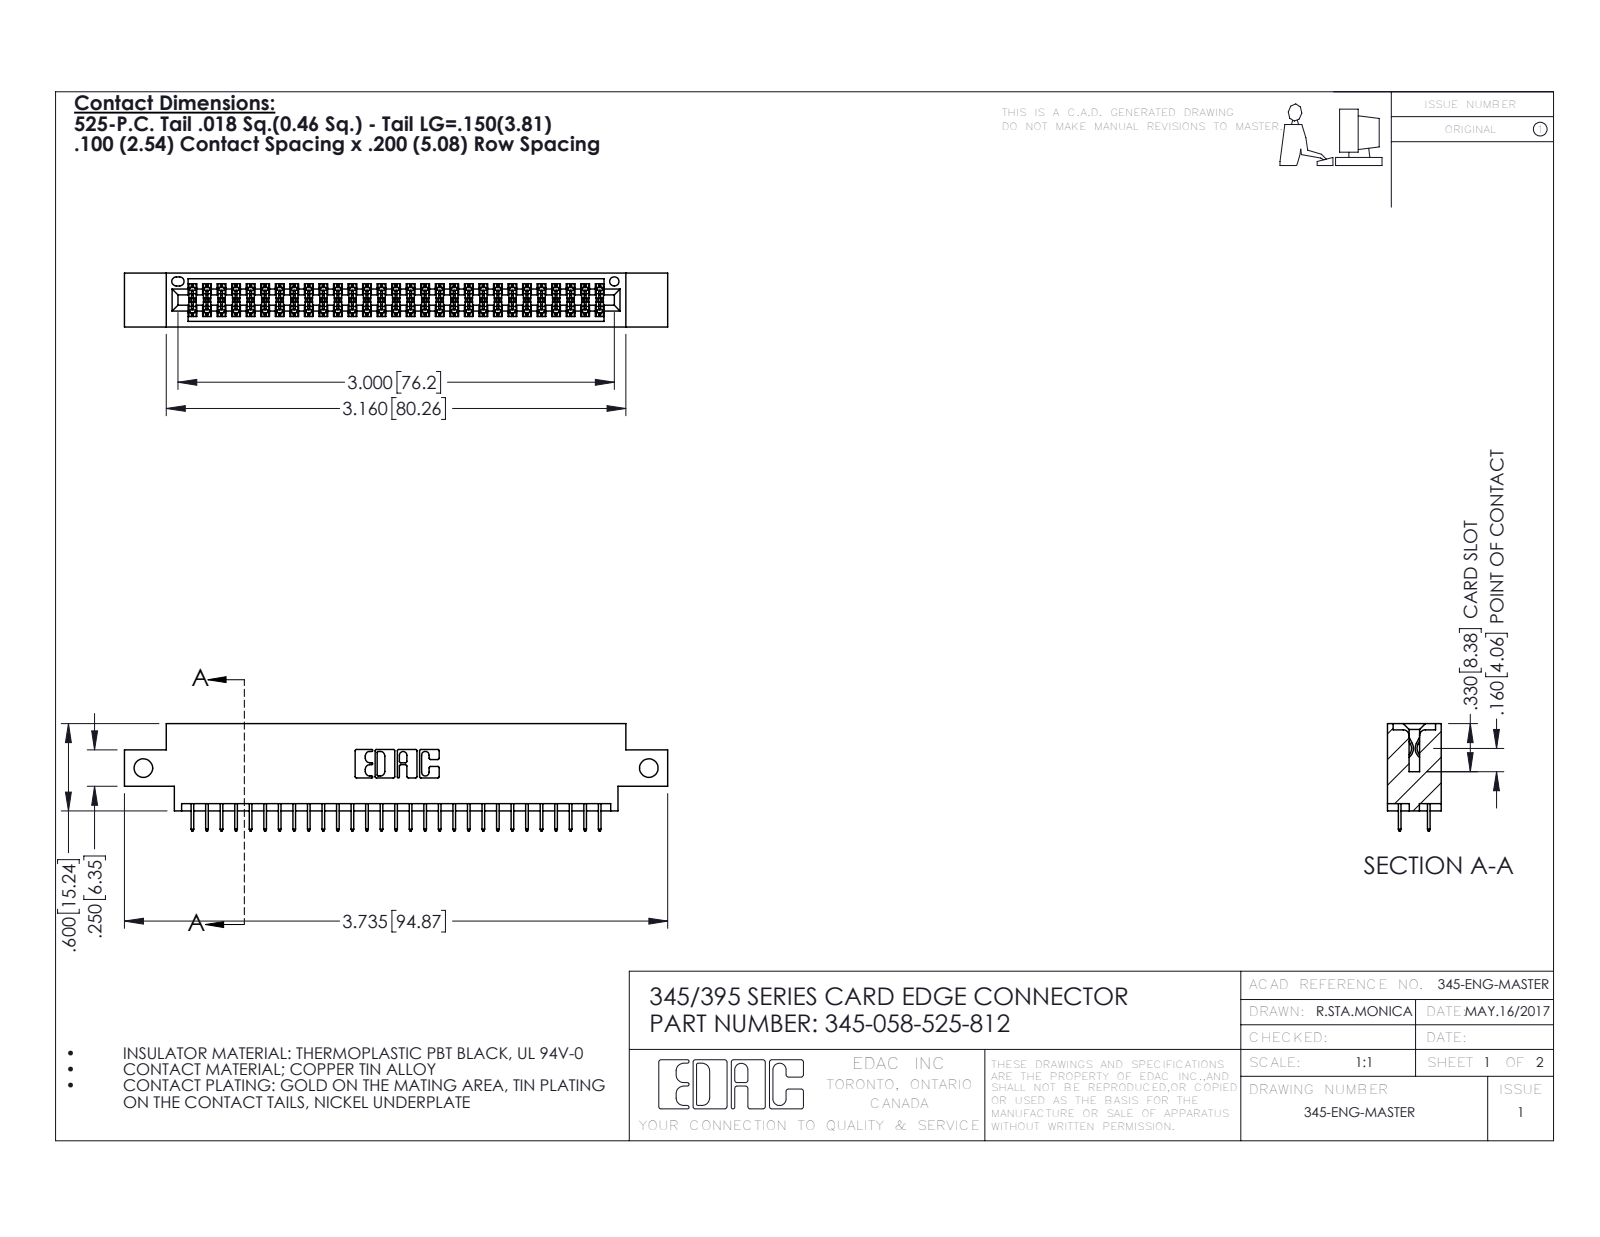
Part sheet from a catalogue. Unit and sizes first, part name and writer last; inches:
Units: inches
Overall size (bounding box): 3.735 × 0.737 × 0.37
Round holes (diameter × count): ⌀0.128 ×2, ⌀0.064 ×1
Partial cylindrical surfaces — rounded edges, fillets, slot ends (radius × count): R0.006 ×87, R0.01 ×22, R0.007 ×6, R0.031 ×6, R0.026 ×3, R0.014 ×2, R0.019 ×2, R0.022 ×2
Main face-to-face distances: 0.072, 0.298, 0.37, 0.2, 0.098, 0.272, 0.025, 0.225, 0.175, 0.072
Hole centre spacings: 3.475
Volume: 0.537 in³ · Surface area: 19.34 in²
Bodies: 59 solids, 3262 faces (2346 planar, 916 cylindrical, 0 other)
Part name (STEP PRODUCT): 345-292-001_345-293-125; 345 Part_0.170 Offset - Side Mount; 345-058-525-812
STEP written by: SolidWorks 2020 (CONFIG_CONTROL_DESIGN)
